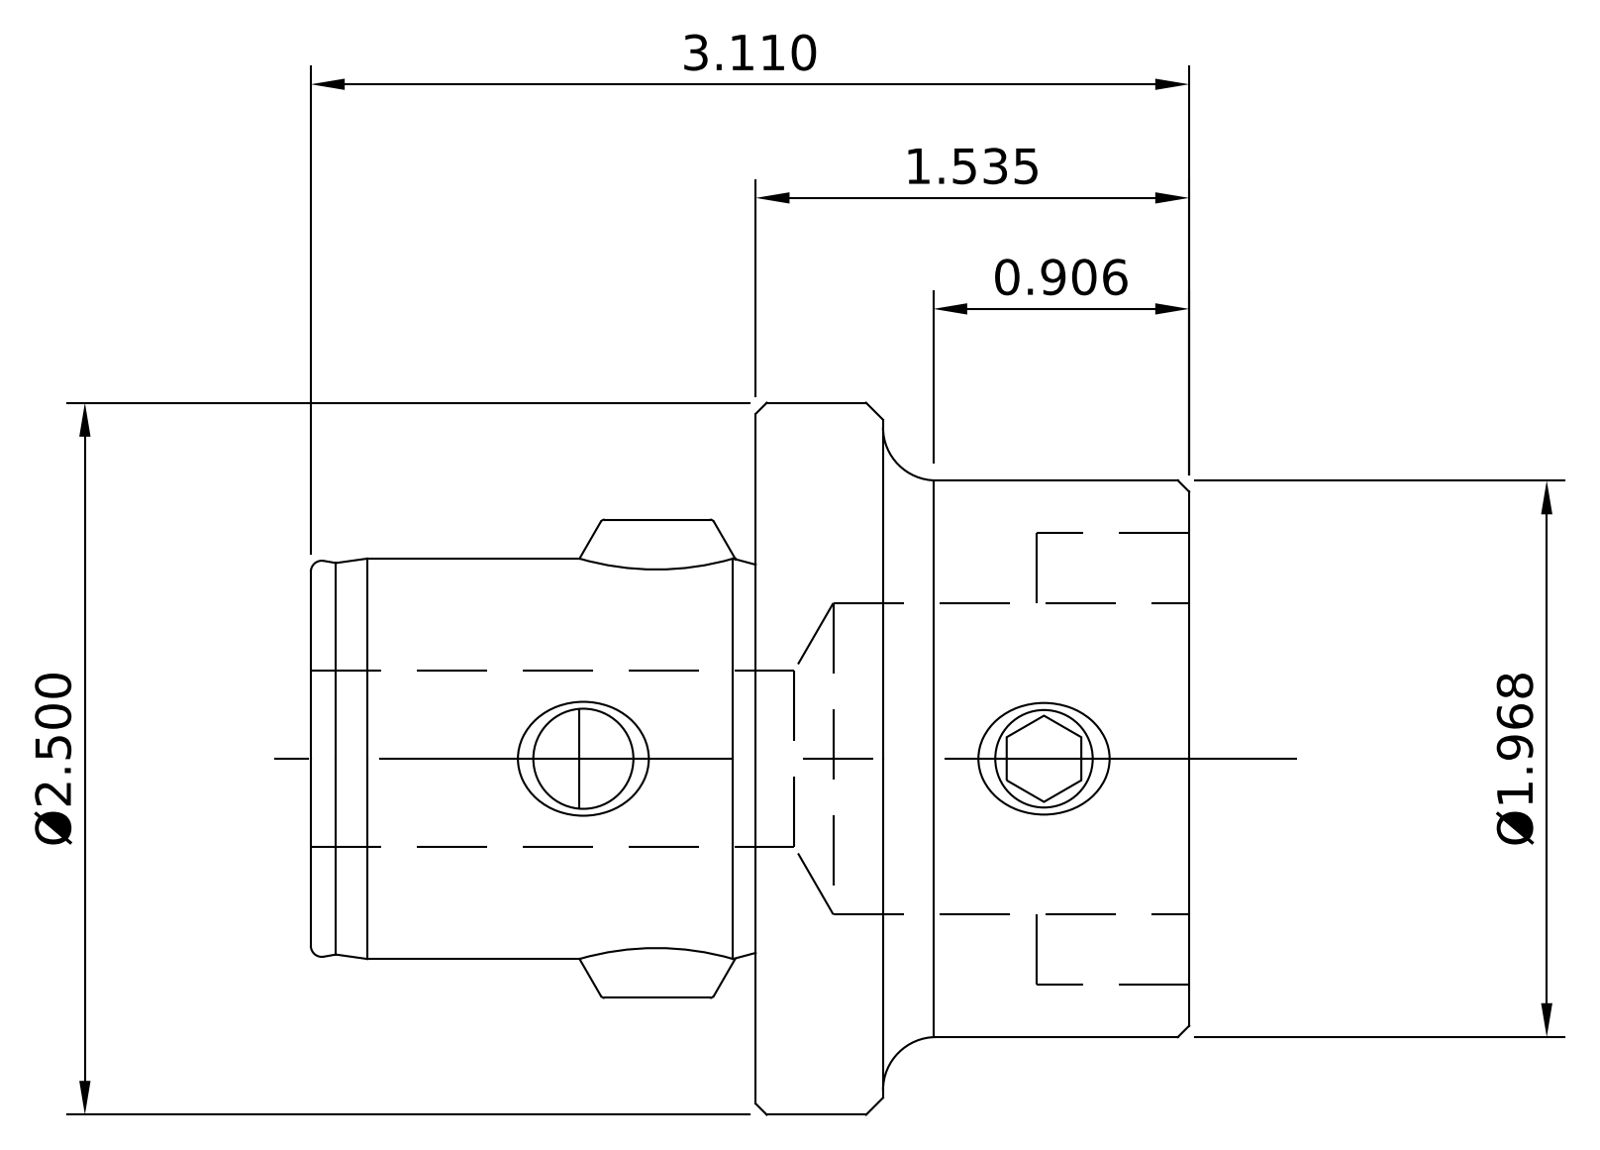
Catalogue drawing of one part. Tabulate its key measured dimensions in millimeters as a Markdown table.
| quantity | value |
| --- | --- |
| part name | 10.691.50X_10.691.506; 11.332.651; 691-50XRing_10.691.506Ring; 10.690.43X_10.690.435 (+1 more) |
| STEP written by | SolidWorks 2014 (AUTOMOTIVE_DESIGN) |
| units | millimeters |
| bodies | 4 solids, 146 faces (41 planar, 49 cylindrical, 56 other) |
| overall size | 79 × 63.27 × 63.27 |
| volume | 103 929 mm³ |
| surface area | 25 456 mm² |
| round holes (diameter × count) | 5 × 1, 8.5 × 1, 9 × 1, 10.3 × 1, 14 × 1, 16 × 1, 18.5 × 1, 28 × 1, 28.5 × 1 |
| round bosses / shafts (diameter × count) | 63.27 × 1, 50 × 1, 49.6 × 1, 36 × 1, 13.9 × 1, 11.9 × 1, 10 × 1, 9.9 × 1 |
| partial cylindrical surfaces (radius × count) | 4.5 × 2, 18 × 1 |
| main face-to-face distances | 39, 40, 79, 24.1, 52, 12, 27, 65.4, 25.4, 13.4 |
| hole center spacings | 19.5, 41.45 |
